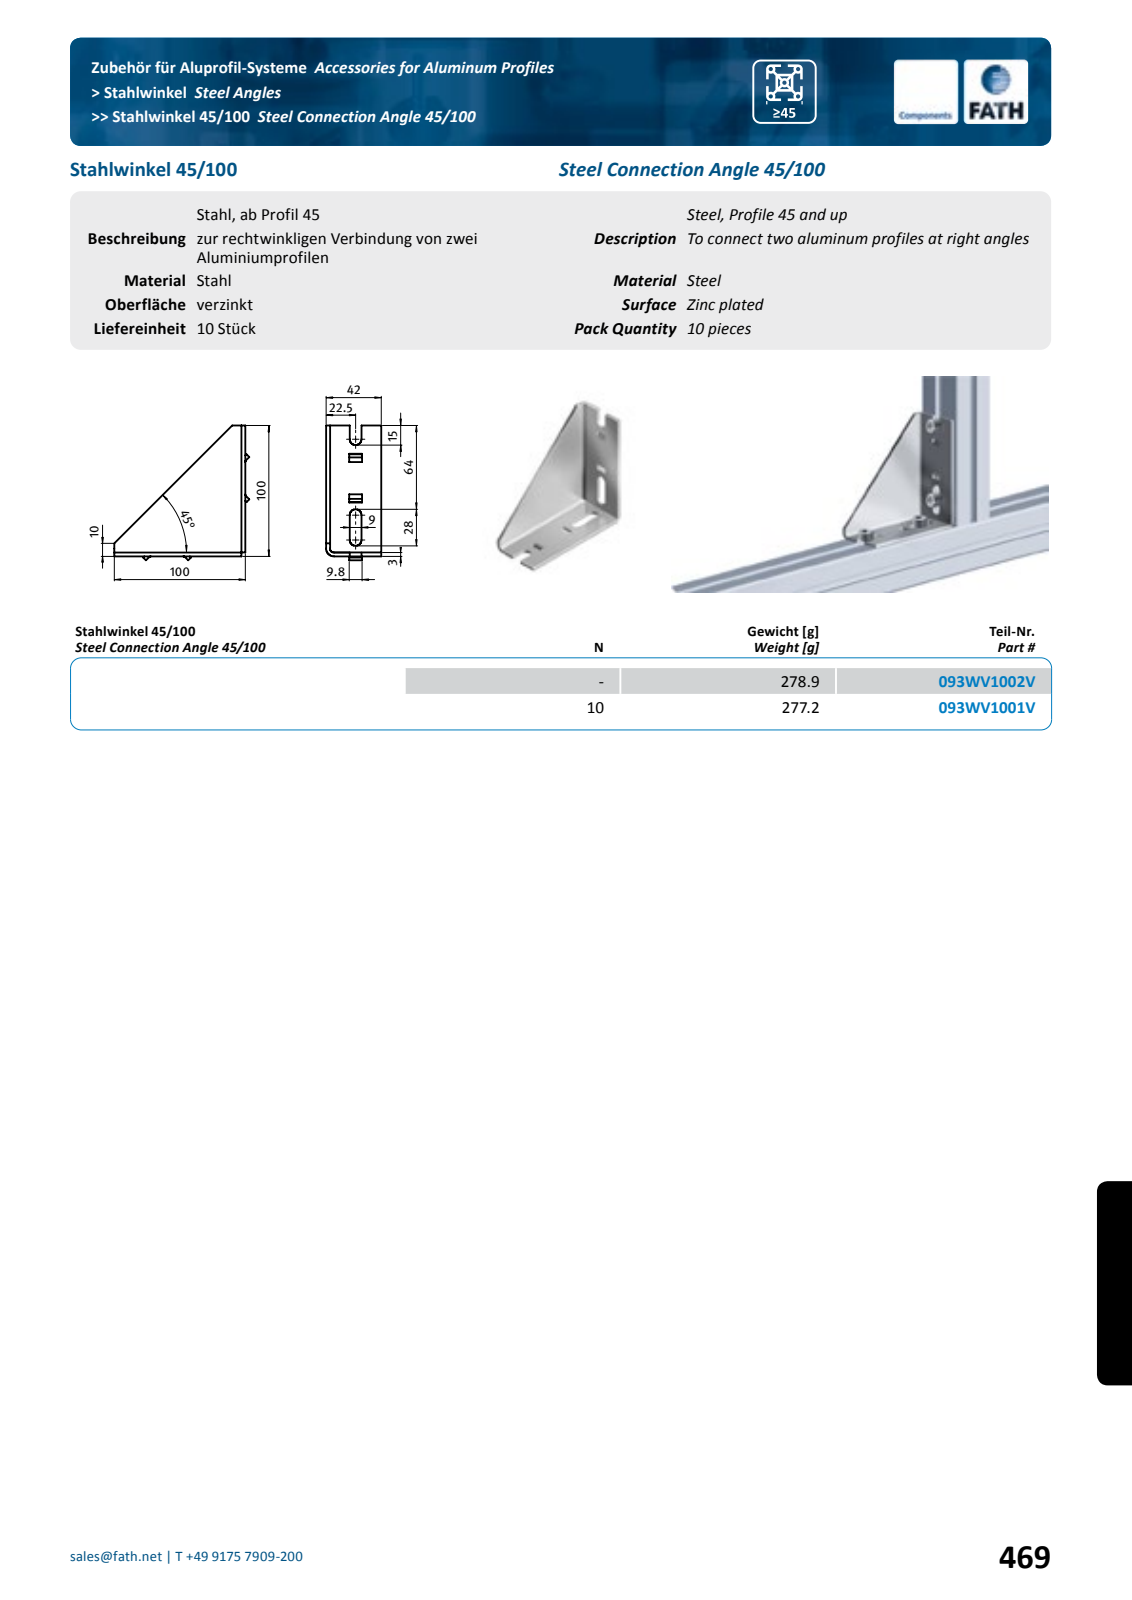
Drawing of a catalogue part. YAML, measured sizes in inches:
part_name: "fath_093wv1001v"
step_written_by: "Spatial InterOp 3D (automotive_design)"
units: inches
bodies: {solids: 1, faces: 119, planar: 79, cylindrical: 40, other: 0}
overall_size: [4.055, 4.055, 1.654]
volume: 2.273
surface_area: 42.23
partial_cylinders:
  - {radius: 0.079, count: 12}
  - {radius: 0.08, count: 8}
  - {radius: 0.177, count: 6}
  - {radius: 0.197, count: 4}
  - {radius: 0.118, count: 2}
  - {radius: 0.236, count: 2}
face_to_face_distances: [0.118, 1.535, 1.654, 0.591, 0.945, 0.119, 3.819, 3.819, 3.937, 0.354]
